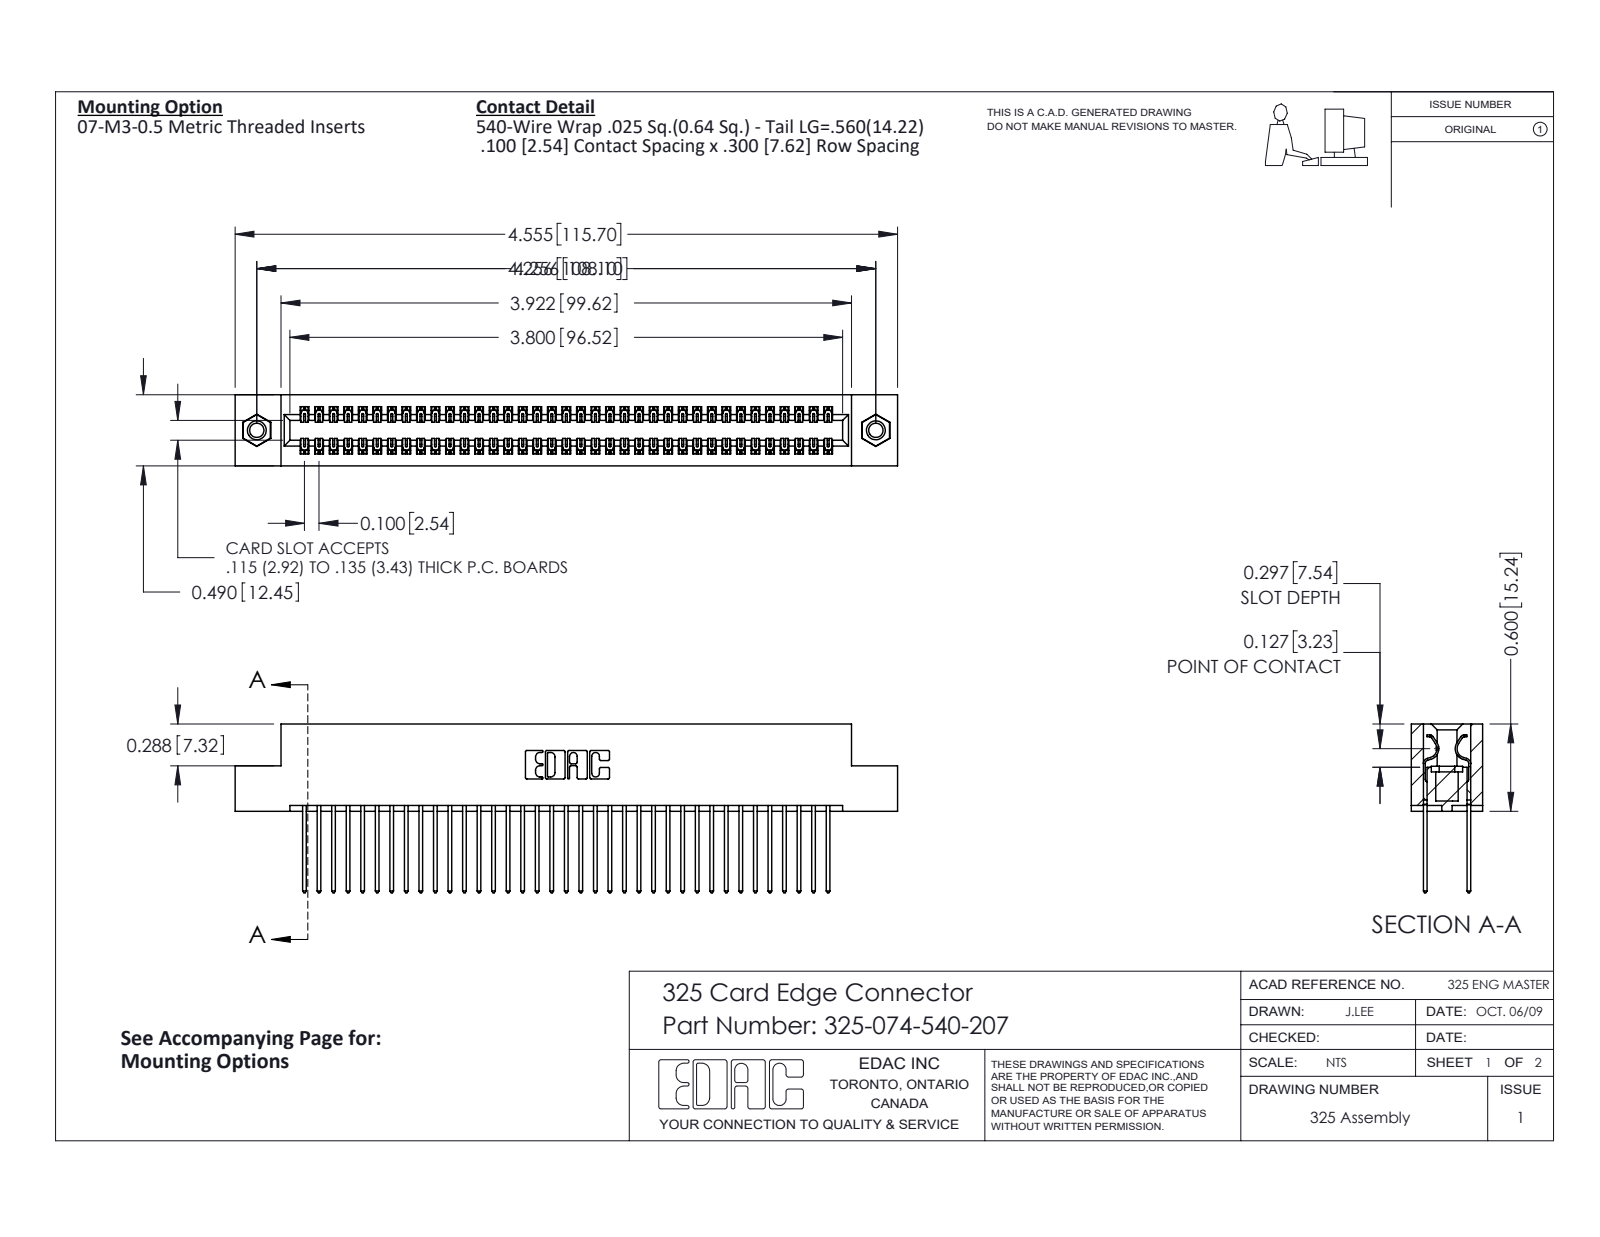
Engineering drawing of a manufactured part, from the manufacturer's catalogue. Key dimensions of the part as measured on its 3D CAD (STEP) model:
Part name (STEP PRODUCT): 325 Part_TI; 345-250-001_345-250-005-103; 325-074-540-207; 325-292-001_325-293-140
STEP written by: SolidWorks 2016 (CONFIG_CONTROL_DESIGN)
Units: inches
Bodies: 77 solids, 4022 faces (2766 planar, 1240 cylindrical, 16 other)
Overall size (bounding box): 4.555 × 1.16 × 0.49
Volume: 0.925 in³ · Surface area: 30.36 in²
Round holes (diameter × count): ⌀0.098 ×2, ⌀0.125 ×2, ⌀0.16 ×2
Round bosses / shafts (diameter × count): ⌀0.155 ×2
Partial cylindrical surfaces — rounded edges, fillets, slot ends (radius × count): R0.006 ×111, R0.01 ×74, R0.01 ×22, R0.007 ×6, R0.031 ×6, R0.026 ×3, R0.014 ×2, R0.022 ×2
Main face-to-face distances: 0.083, 0.407, 0.3, 0.107, 0.383, 0.025, 0.49, 0.325, 0.275, 0.56
Hole centre spacings: 4.256
